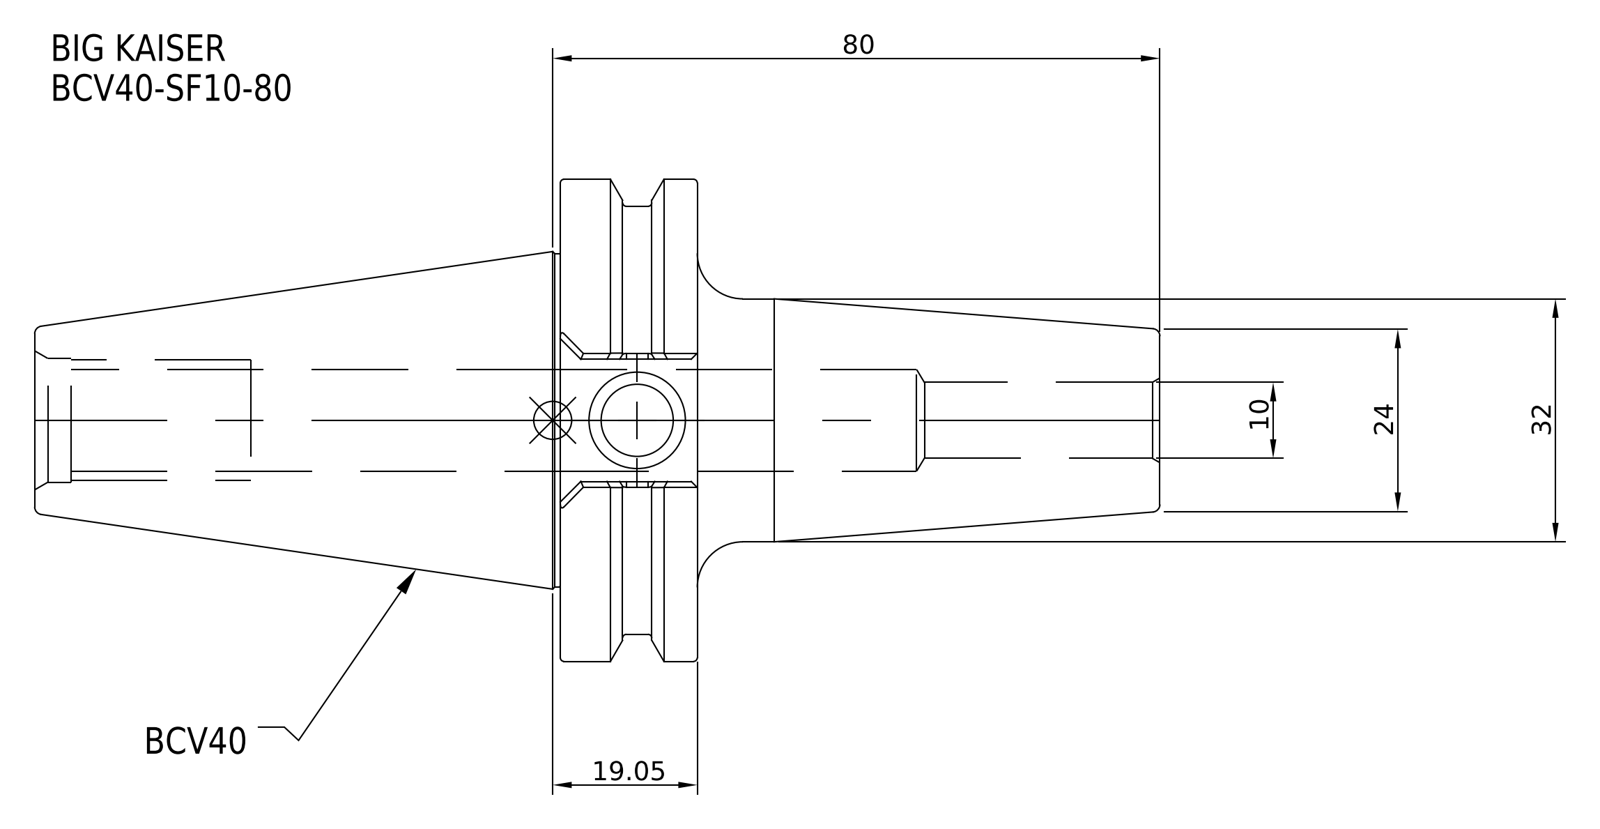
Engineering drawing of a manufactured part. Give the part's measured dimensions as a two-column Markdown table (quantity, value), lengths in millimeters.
| quantity | value |
| --- | --- |
| part name | BCV40-SF10-80 |
| STEP written by | SolidWorks 2021 (CONFIG_CONTROL_DESIGN) |
| units | millimeters |
| bodies | 1 solid, 27 faces (7 planar, 12 cylindrical, 8 other) |
| overall size | 148.25 × 63.5 × 63.5 |
| volume | 158 045 mm³ |
| surface area | 23 378 mm² |
| round holes (diameter × count) | 10 × 1 |
| round bosses / shafts (diameter × count) | 63.5 × 1, 56.36 × 1, 44.45 × 1, 32 × 1 |
| main face-to-face distances | 18.05, 87.3, 69.25, 60.95, 79, 148.25, 66.95, 6, 12.05, 81.3 |
